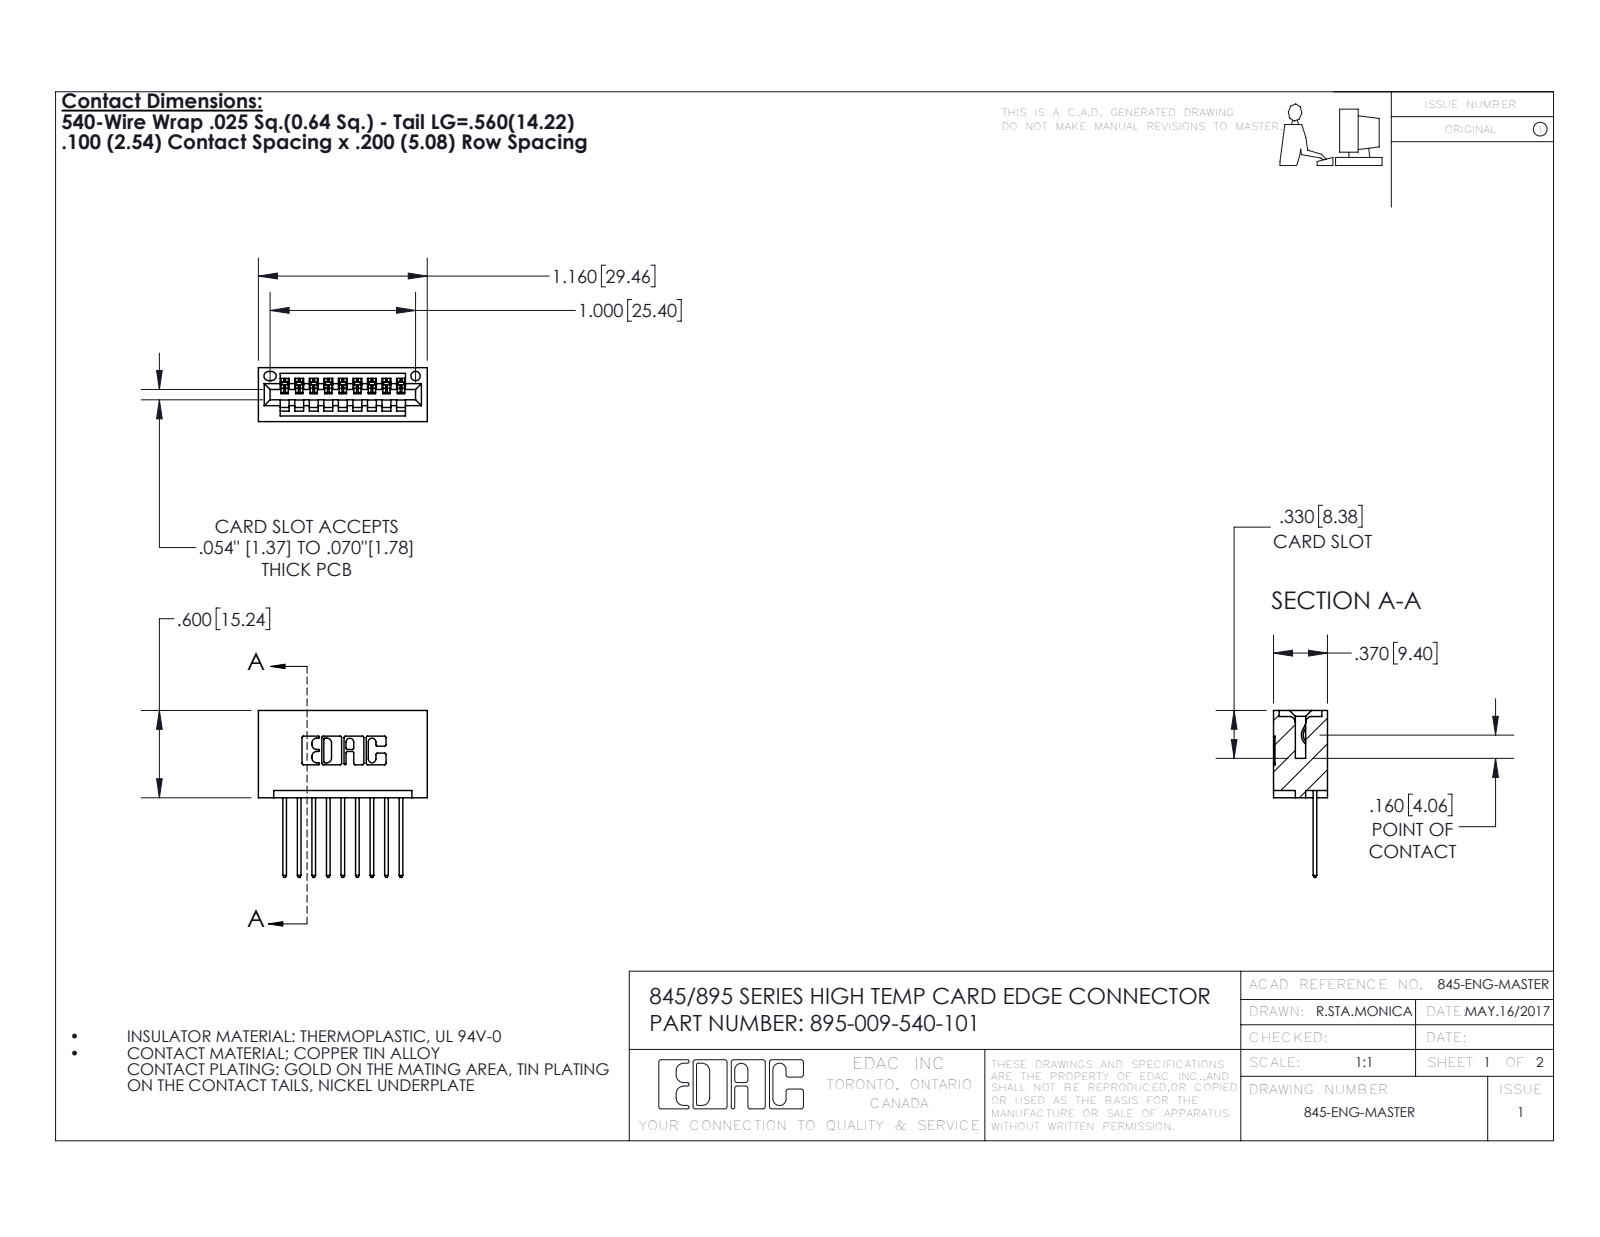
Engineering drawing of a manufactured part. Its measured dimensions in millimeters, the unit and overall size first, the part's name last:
Units: millimetres
Overall size (bounding box): 29.5 × 29.1 × 9.4
Round holes (diameter × count): ⌀1.6 ×1
Partial cylindrical surfaces — rounded edges, fillets, slot ends (radius × count): R0.3 ×22, R0.2 ×18, R0.3 ×18, R0.2 ×6, R0.8 ×6, R0.7 ×3, R0.8 ×2, R1 ×2
Main face-to-face distances: 5.1, 7.6, 1.8, 2.5, 9.4, 7.6, 2.5, 6.9, 0.6, 10.2
Volume: 3 130 mm³ · Surface area: 3 982 mm²
Bodies: 10 solids, 640 faces (436 planar, 204 cylindrical, 0 other)
Part name (STEP PRODUCT): 345-292-001_345-293-140; 345 Part_No Mounting Lugs; 395-009-540-101
STEP written by: SolidWorks 2016 (CONFIG_CONTROL_DESIGN)
